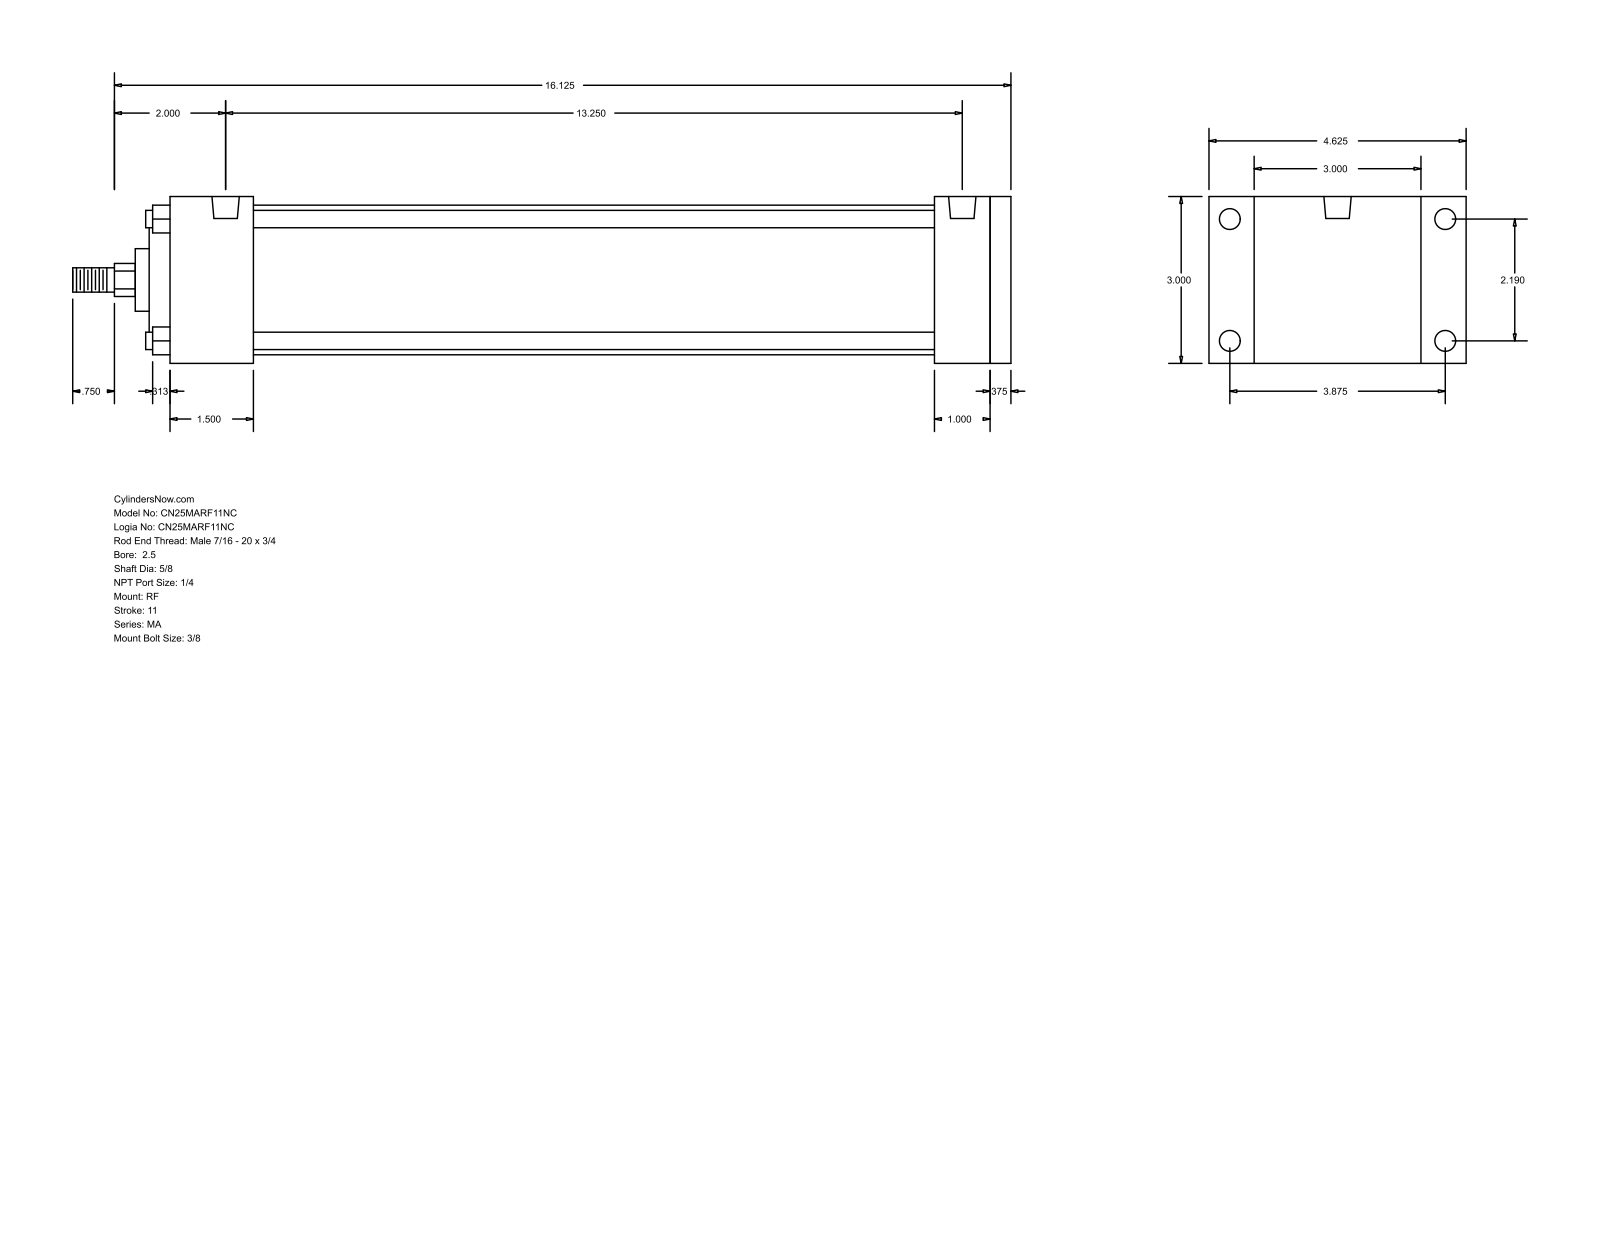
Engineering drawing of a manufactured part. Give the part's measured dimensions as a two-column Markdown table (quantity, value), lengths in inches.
| quantity | value |
| --- | --- |
| part name | MA_RF__0250_0.625 |
| STEP written by | GSSL Pune (CONFIG_CONTROL_DESIGN) |
| units | inches |
| bodies | 0 solids, 94 faces (65 planar, 29 cylindrical, 0 other) |
| overall size | 16.875 × 4.625 × 3 |
| round holes (diameter × count) | 0.313 × 4, 0.375 × 4, 0.492 × 2 |
| round bosses / shafts (diameter × count) | 0.313 × 4, 2.69 × 1, 2 × 1, 1.125 × 1, 0.625 × 1, 0.437 × 1 |
| partial cylindrical surfaces (radius × count) | 0.297 × 1 |
| main face-to-face distances | 3, 15.125, 0.375, 14.75, 1, 1.5, 13.75, 12.25, 13.25, 13.625 |
| hole center spacings | 2.19, 3.875, 4.451, 13.25 |
